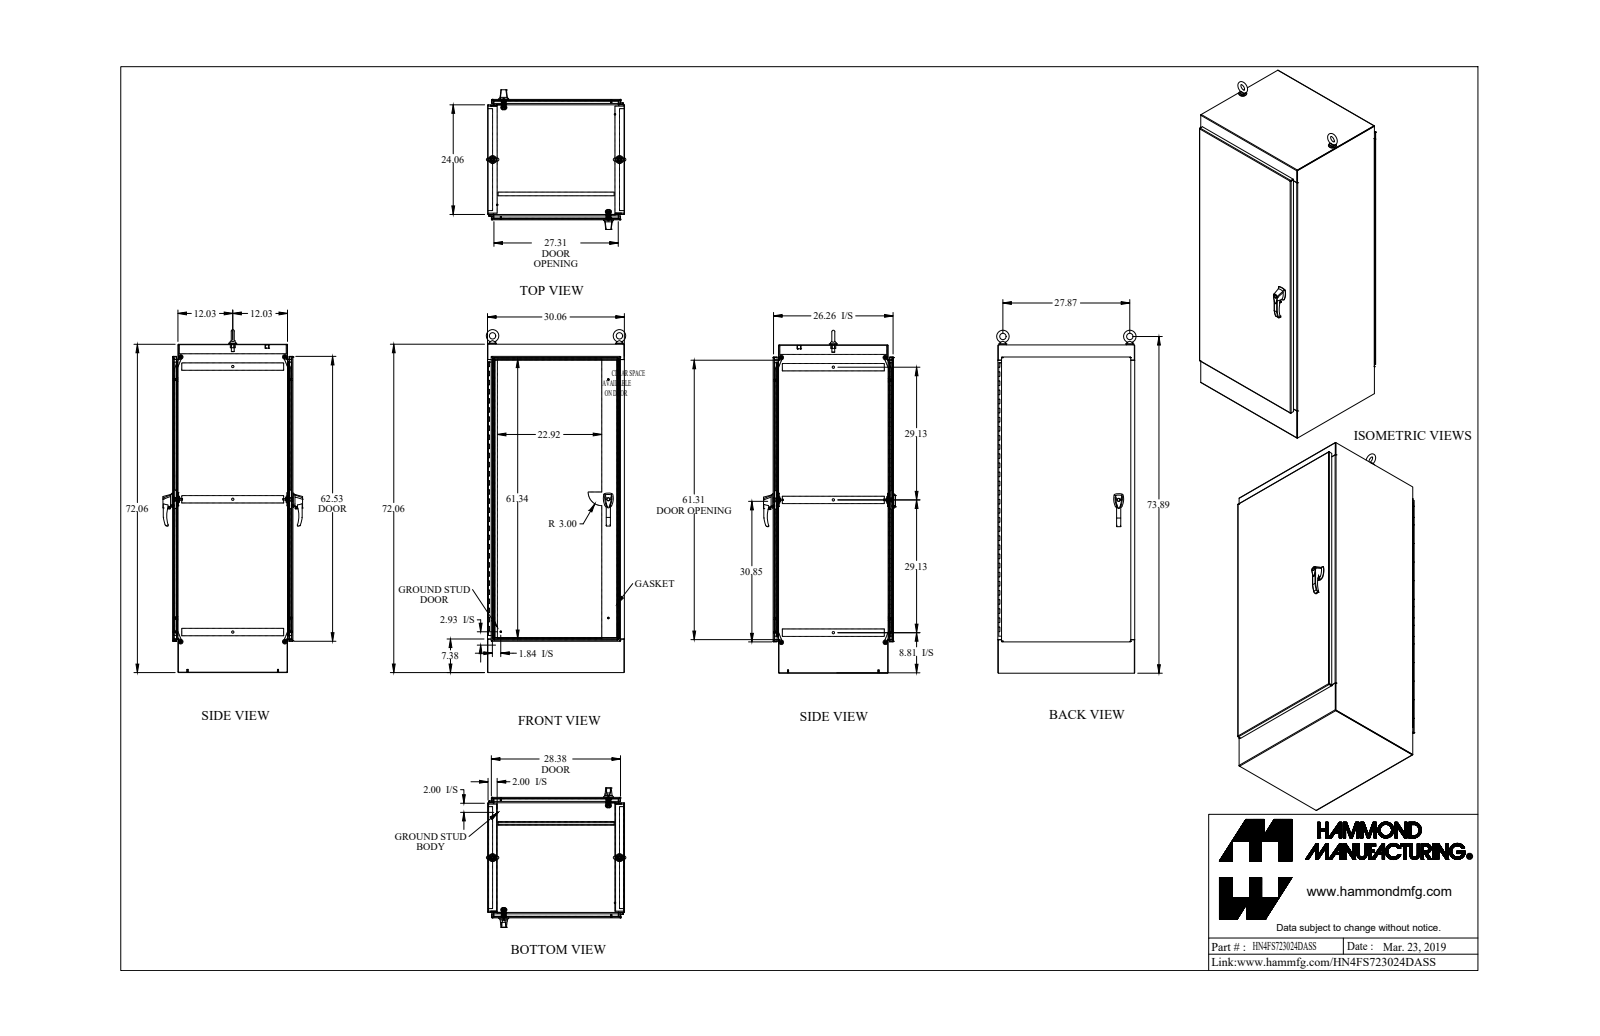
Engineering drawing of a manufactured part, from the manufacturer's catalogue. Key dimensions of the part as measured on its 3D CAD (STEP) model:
Part name (STEP PRODUCT): HN4FS723024DASS
STEP written by: SolidWorks 2018 (AUTOMOTIVE_DESIGN)
Units: inches
Bodies: 84 solids, 3176 faces (1425 planar, 1483 cylindrical, 268 other)
Overall size (bounding box): 75.256 × 30.664 × 30.604
Volume: 1 153 in³ · Surface area: 24 287 in²
Round holes (diameter × count): ⌀0.304 ×20, ⌀0.35 ×8, ⌀0.25 ×4, ⌀0.257 ×4, ⌀0.28 ×4, ⌀0.281 ×4, ⌀0.313 ×4, ⌀0.39 ×4, ⌀0.413 ×4, ⌀0.5 ×3, ⌀0.11 ×2, ⌀0.173 ×2
Round bosses / shafts (diameter × count): ⌀1 ×4, ⌀0.75 ×4, ⌀0.63 ×4, ⌀0.625 ×4, ⌀0.44 ×4, ⌀0.37 ×4, ⌀0.313 ×4, ⌀0.281 ×4
Partial cylindrical surfaces — rounded edges, fillets, slot ends (radius × count): R0.125 ×44, R0.043 ×42, R0.138 ×36, R0.018 ×32, R0.048 ×26, R0.143 ×26, R0.5 ×26, R0.06 ×21
Main face-to-face distances: 0.095, 26.339, 29.965, 29.87, 1.187, 25.152, 26.244, 26.434, 30.06, 71.965
Hole centre spacings: 6, 28.957, 12, 30.765, 18, 33.563, 24, 37.128
